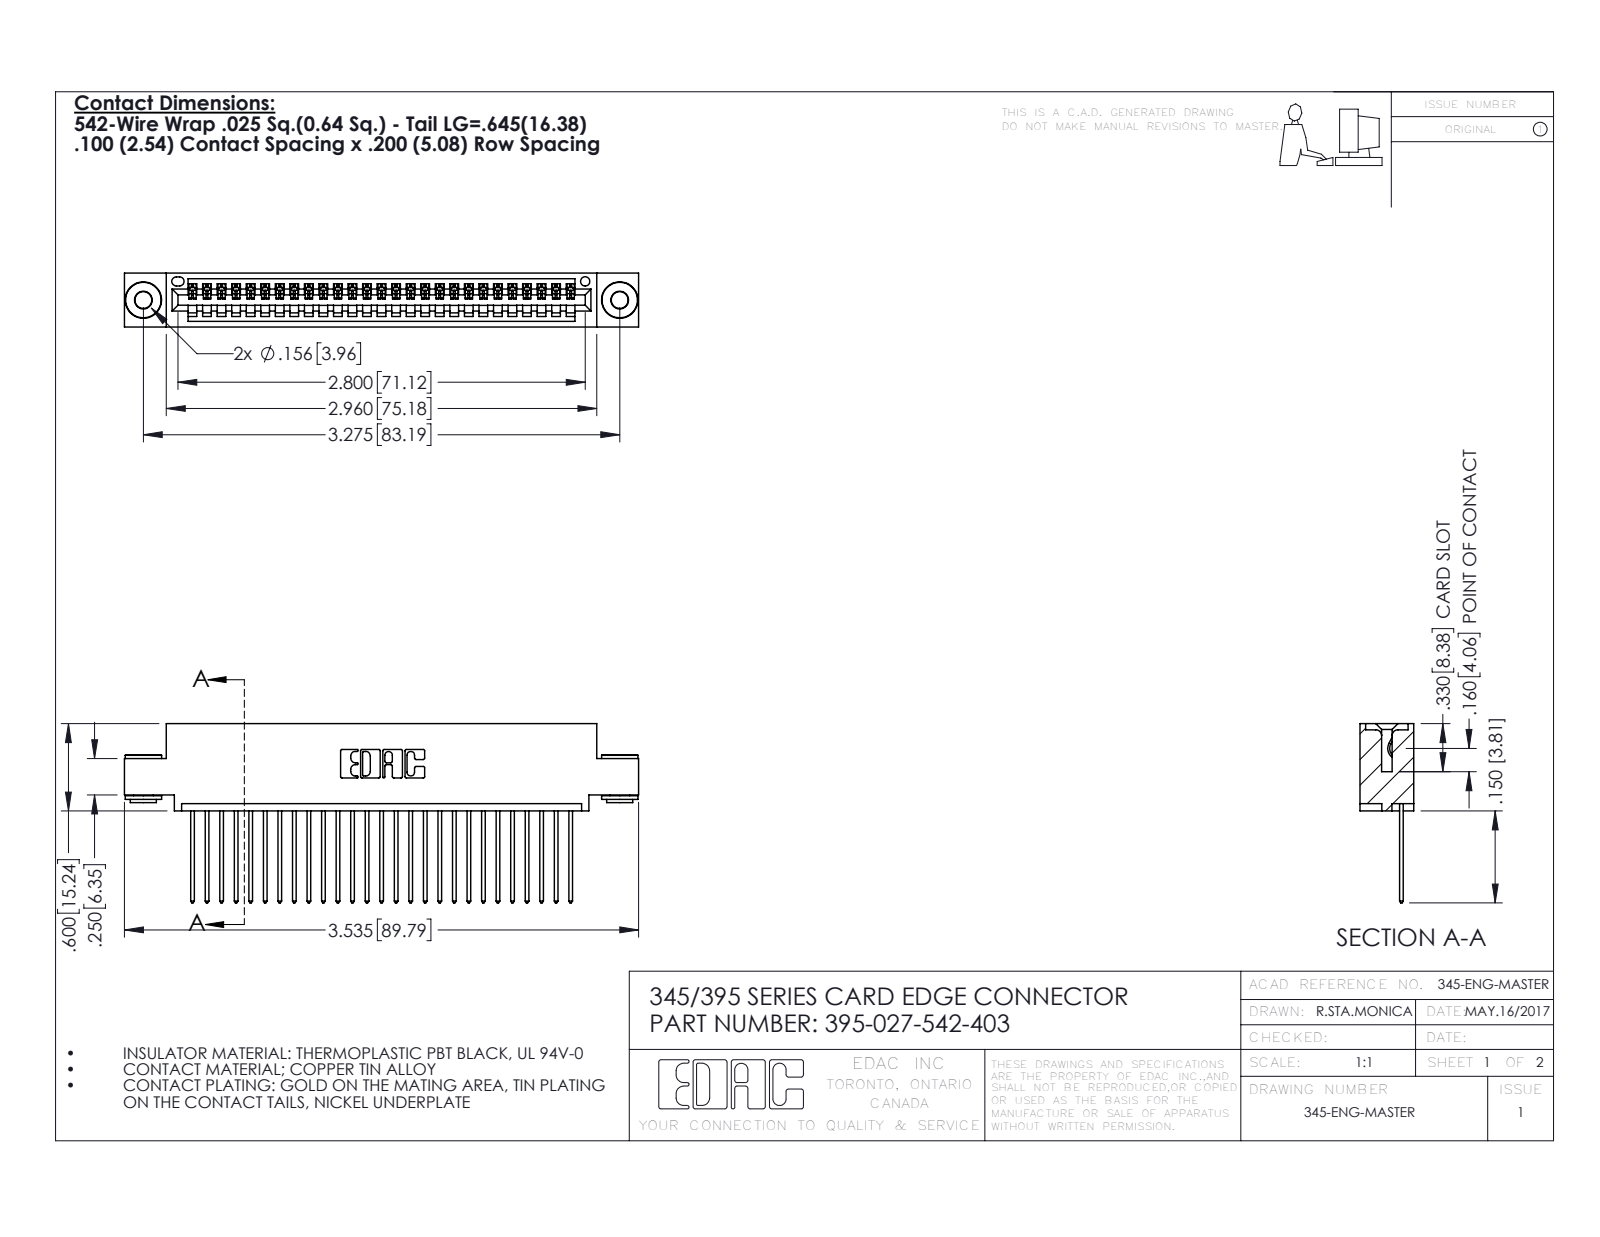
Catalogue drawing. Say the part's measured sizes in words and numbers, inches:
The part is named "345-250-002_345-250-002-102; 345 Part_0.110 Offset - 0.156 Dia-TH; 345-292-001_345-293-142; 395-027-542-403". Its 3-D file was written by "SolidWorks 2016 (CONFIG_CONTROL_DESIGN)". It is 30 solids with 1734 faces: 1174 planar, 552 cylindrical and 8 other. Overall it measures 3.535 by 1.232 by 0.37 inches. Its volume is 0.513 cubic inches and its surface area 18.06 square inches. Round holes: 2 of diameter 0.116, 2 of diameter 0.156, 1 of diameter 0.064. Round bosses or shafts: 2 of diameter 0.25, 2 of diameter 0.18, 2 of diameter 0.136. Partial cylindrical surfaces (rounded edges, fillets, slot ends): 54 of radius 0.006, 54 of radius 0.01, 22 of radius 0.01, 6 of radius 0.007, 6 of radius 0.031, 3 of radius 0.026, 2 of radius 0.031, 2 of radius 0.04. The main face-to-face distances are 0.072, 0.298, 0.025, 0.37, 0.098, 0.272, 0.2, 0.225, 0.149, 0.072. The hole center spacings are 0.27, 3.04, 3.275.
